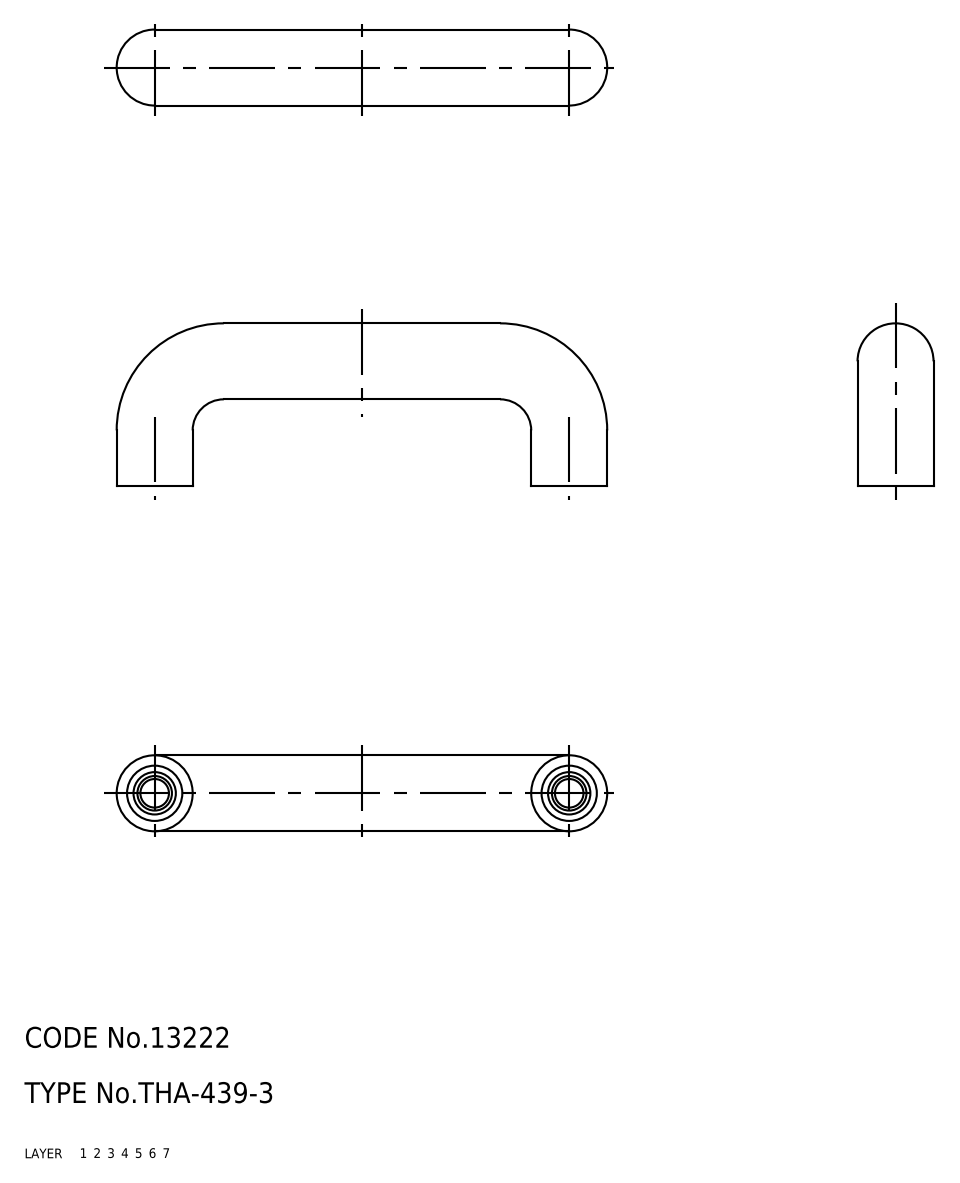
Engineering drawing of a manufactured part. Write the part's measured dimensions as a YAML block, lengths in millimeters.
part_name: "pull; coat; THA_439_3_1652_36"
step_written_by: "CADfix (AUTOMOTIVE_DESIGN)"
units: millimeters
bodies: {solids: 2, faces: 40, planar: 0, cylindrical: 0, other: 40}
overall_size: [71, 23.5, 11]
volume: 7936
surface_area: 7923
